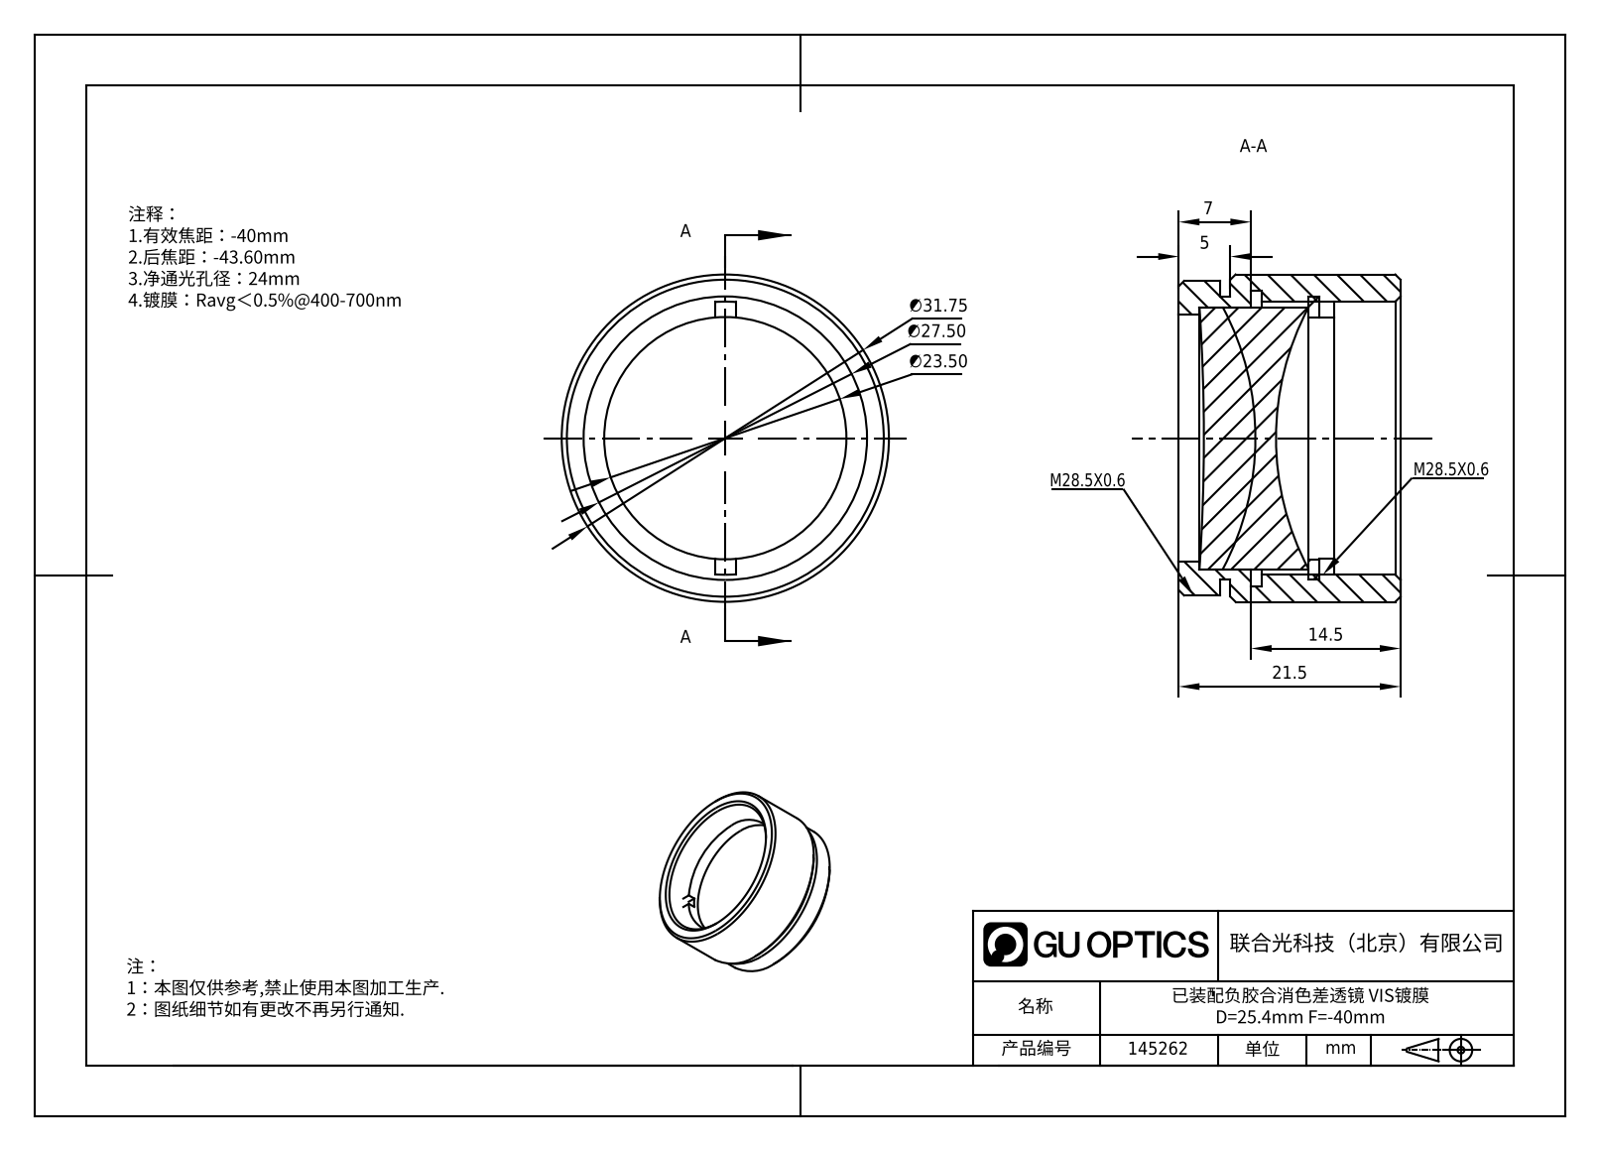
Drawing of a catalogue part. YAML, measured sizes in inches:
part_name: "145262"
step_written_by: "SolidWorks 2020 (CONFIG_CONTROL_DESIGN)"
units: inches
bodies: {solids: 4, faces: 54, planar: 16, cylindrical: 22, other: 16}
overall_size: [1.25, 1.25, 0.846]
volume: 0.6
surface_area: 13.33
round_holes:
  - {diameter: 0.925, count: 1}
  - {diameter: 0.945, count: 1}
  - {diameter: 1.043, count: 1}
  - {diameter: 1.13, count: 1}
round_bosses_or_shafts:
  - {diameter: 1.25, count: 1}
  - {diameter: 1.201, count: 1}
  - {diameter: 1.083, count: 1}
  - {diameter: 1, count: 1}
face_to_face_distances: [0.118, 0.079, 0.039, 0.157, 0.197, 0.496, 0.594, 0.098, 0.846, 0.351]
